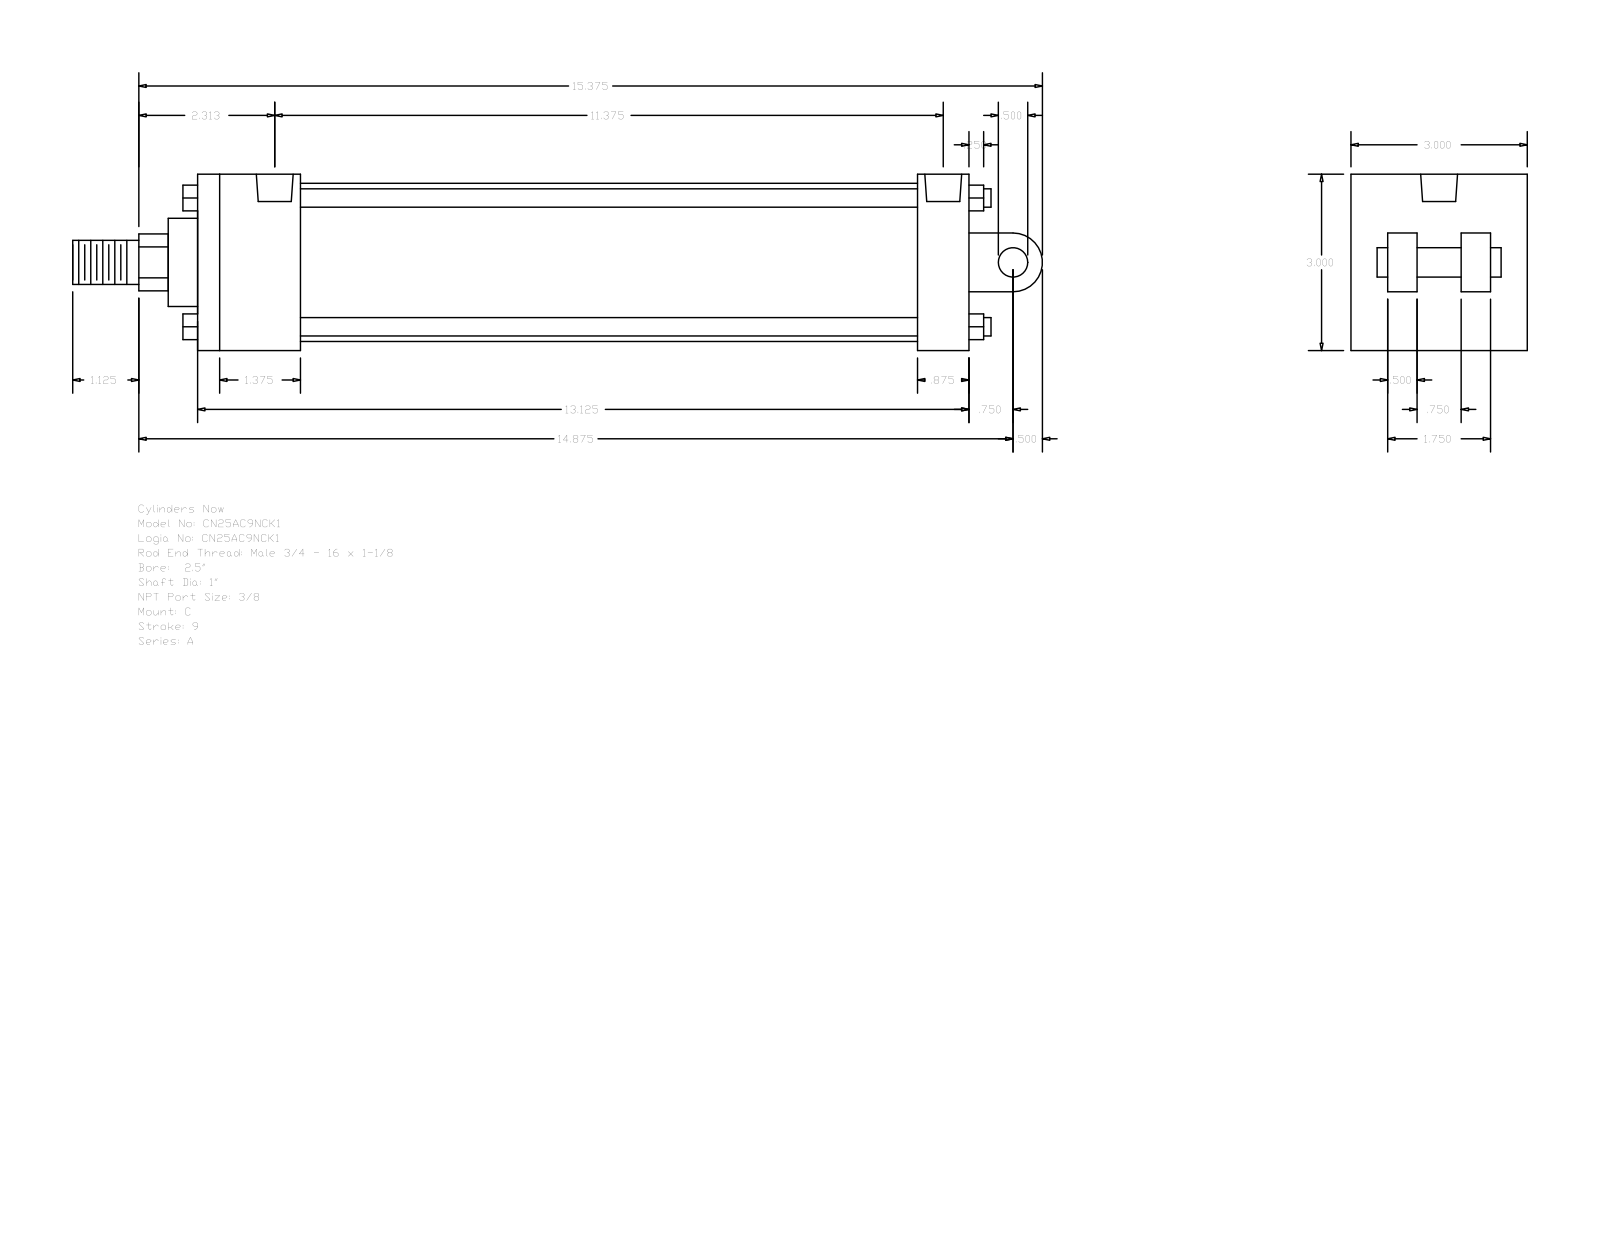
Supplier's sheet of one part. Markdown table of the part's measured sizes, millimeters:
| quantity | value |
| --- | --- |
| part name | A_C__0250_1 |
| STEP written by | GSSL Pune (CONFIG_CONTROL_DESIGN) |
| units | millimeters |
| bodies | 0 solids, 135 faces (102 planar, 33 cylindrical, 0 other) |
| overall size | 419.1 × 76.2 × 76.2 |
| round holes (diameter × count) | 5.56 × 4, 15.93 × 2 |
| round bosses / shafts (diameter × count) | 7.94 × 4, 68.33 × 1, 38.1 × 1, 25.4 × 1, 19.05 × 1, 12.7 × 1 |
| partial cylindrical surfaces (radius × count) | 12.29 × 1, 12.7 × 1 |
| main face-to-face distances | 76.2, 333.37, 12.7, 44.45, 311.15, 266.7, 288.92, 22.22, 15.87, 25.4 |
| hole center spacings | 2.38, 291.3, 293.68, 288.92 |
